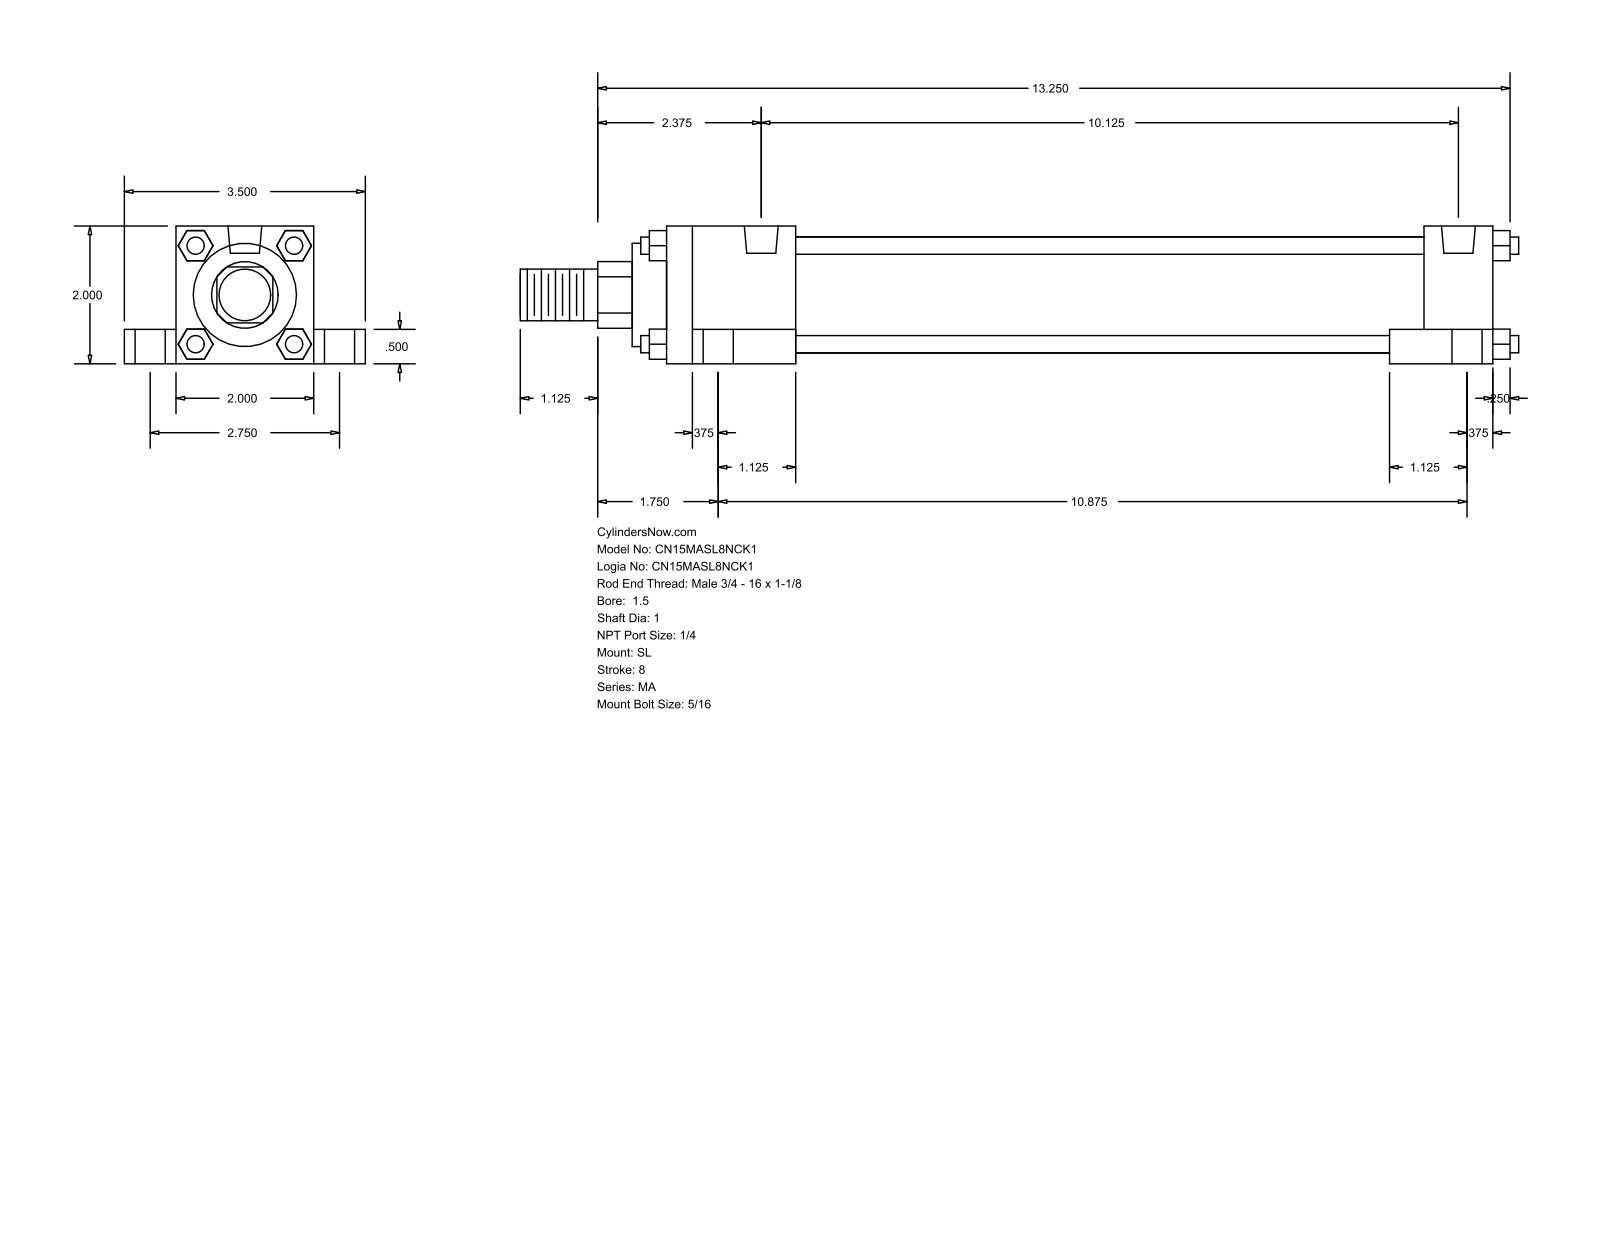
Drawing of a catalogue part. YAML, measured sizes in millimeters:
part_name: "MA_SL__0150_1"
step_written_by: "GSSL Pune (CONFIG_CONTROL_DESIGN)"
units: millimeters
bodies: {solids: 0, faces: 148, planar: 112, cylindrical: 36, other: 0}
overall_size: [368.3, 88.9, 50.8]
round_holes:
  - {diameter: 7.94, count: 4}
  - {diameter: 11.11, count: 4}
  - {diameter: 17.46, count: 4}
  - {diameter: 12.49, count: 2}
round_bosses_or_shafts:
  - {diameter: 6.35, count: 4}
  - {diameter: 42.93, count: 1}
  - {diameter: 38.1, count: 1}
  - {diameter: 25.4, count: 1}
  - {diameter: 19.05, count: 1}
partial_cylinders:
  - {radius: 12.29, count: 1}
face_to_face_distances: [50.8, 12.7, 19.05, 69.85, 38.1, 9.52, 304.8, 25.4, 6.35, 279.4]
hole_center_spacings: [35.06, 38.36, 69.84, 257.17, 262.68, 275.27, 276.23, 284.92]
